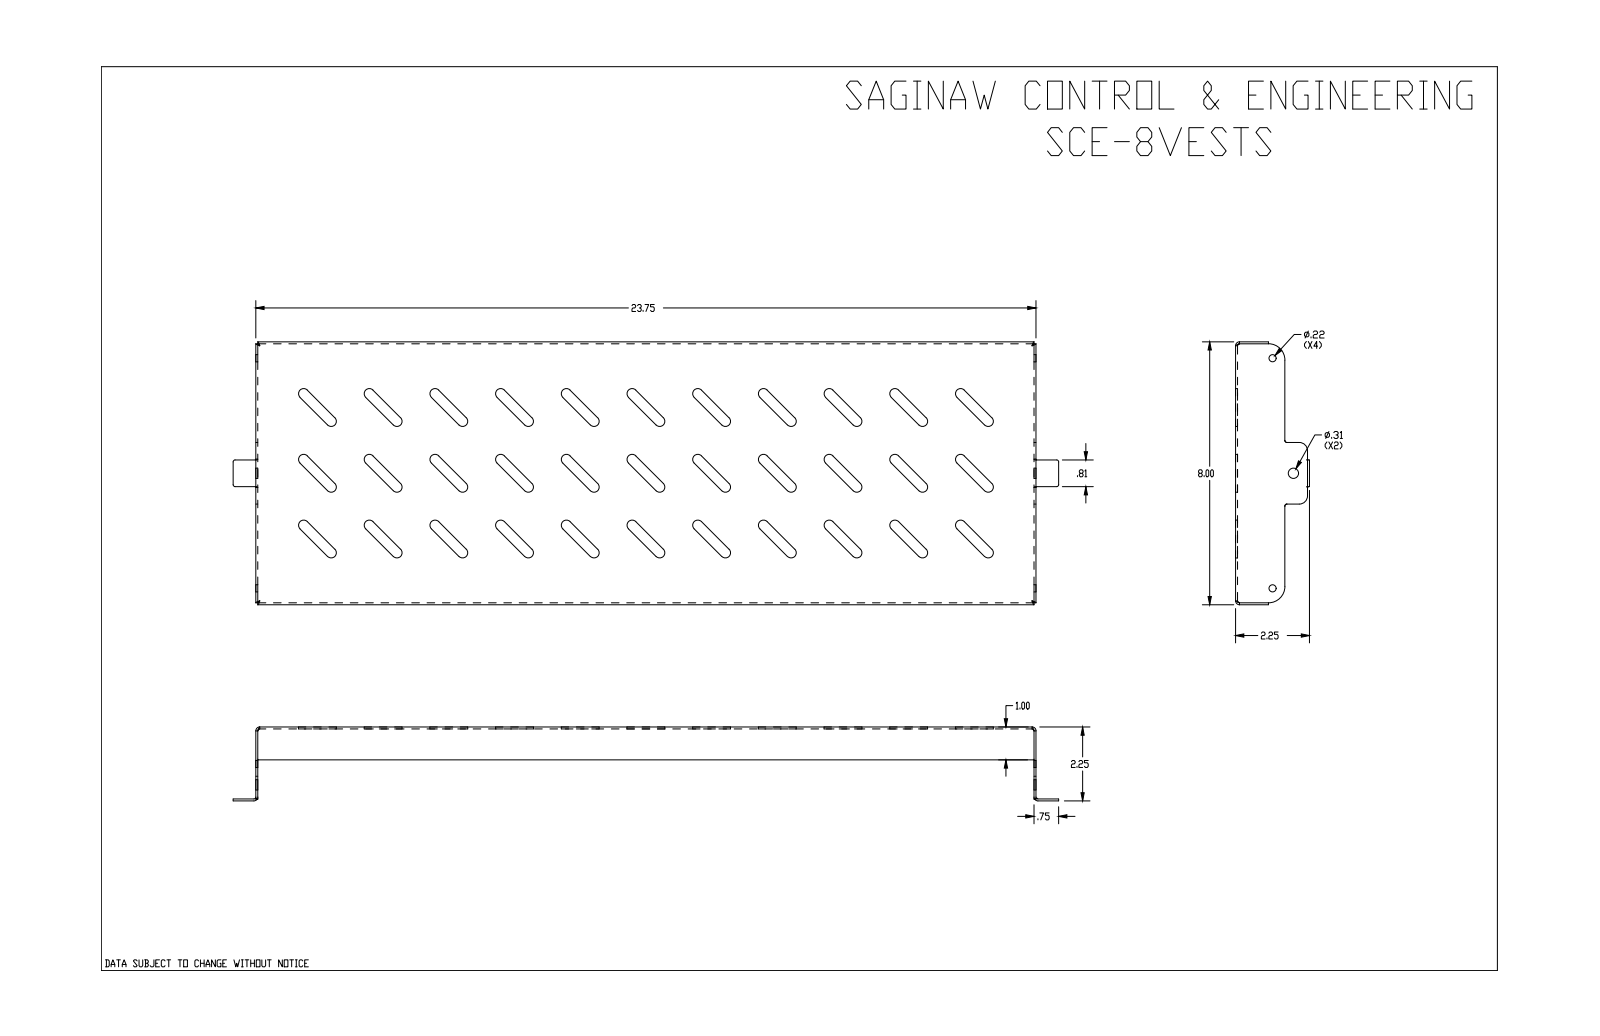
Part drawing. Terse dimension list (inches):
name: SCE-8VESTS
written by: SolidWorks 2019 (CONFIG_CONTROL_DESIGN)
unit: in
bodies: 1 solid, 232 faces (108 planar, 104 cylindrical, 20 other)
size: 25.13 × 8 × 2.25
volume: 14.58 in³; area: 497.7 in²
holes: 2× ⌀0.218, 1× ⌀0.313
rounds: 66× R0.156, 10× R0.06, 6× R0.12, 4× R0.063, 2× R0.02, 2× R0.25, 2× R0.5
face distances: 0.06, 7.94, 23.69, 7.88, 8, 23.63, 23.75, 2.828, 0.94, 1
hole spacings: 3.557, 7
